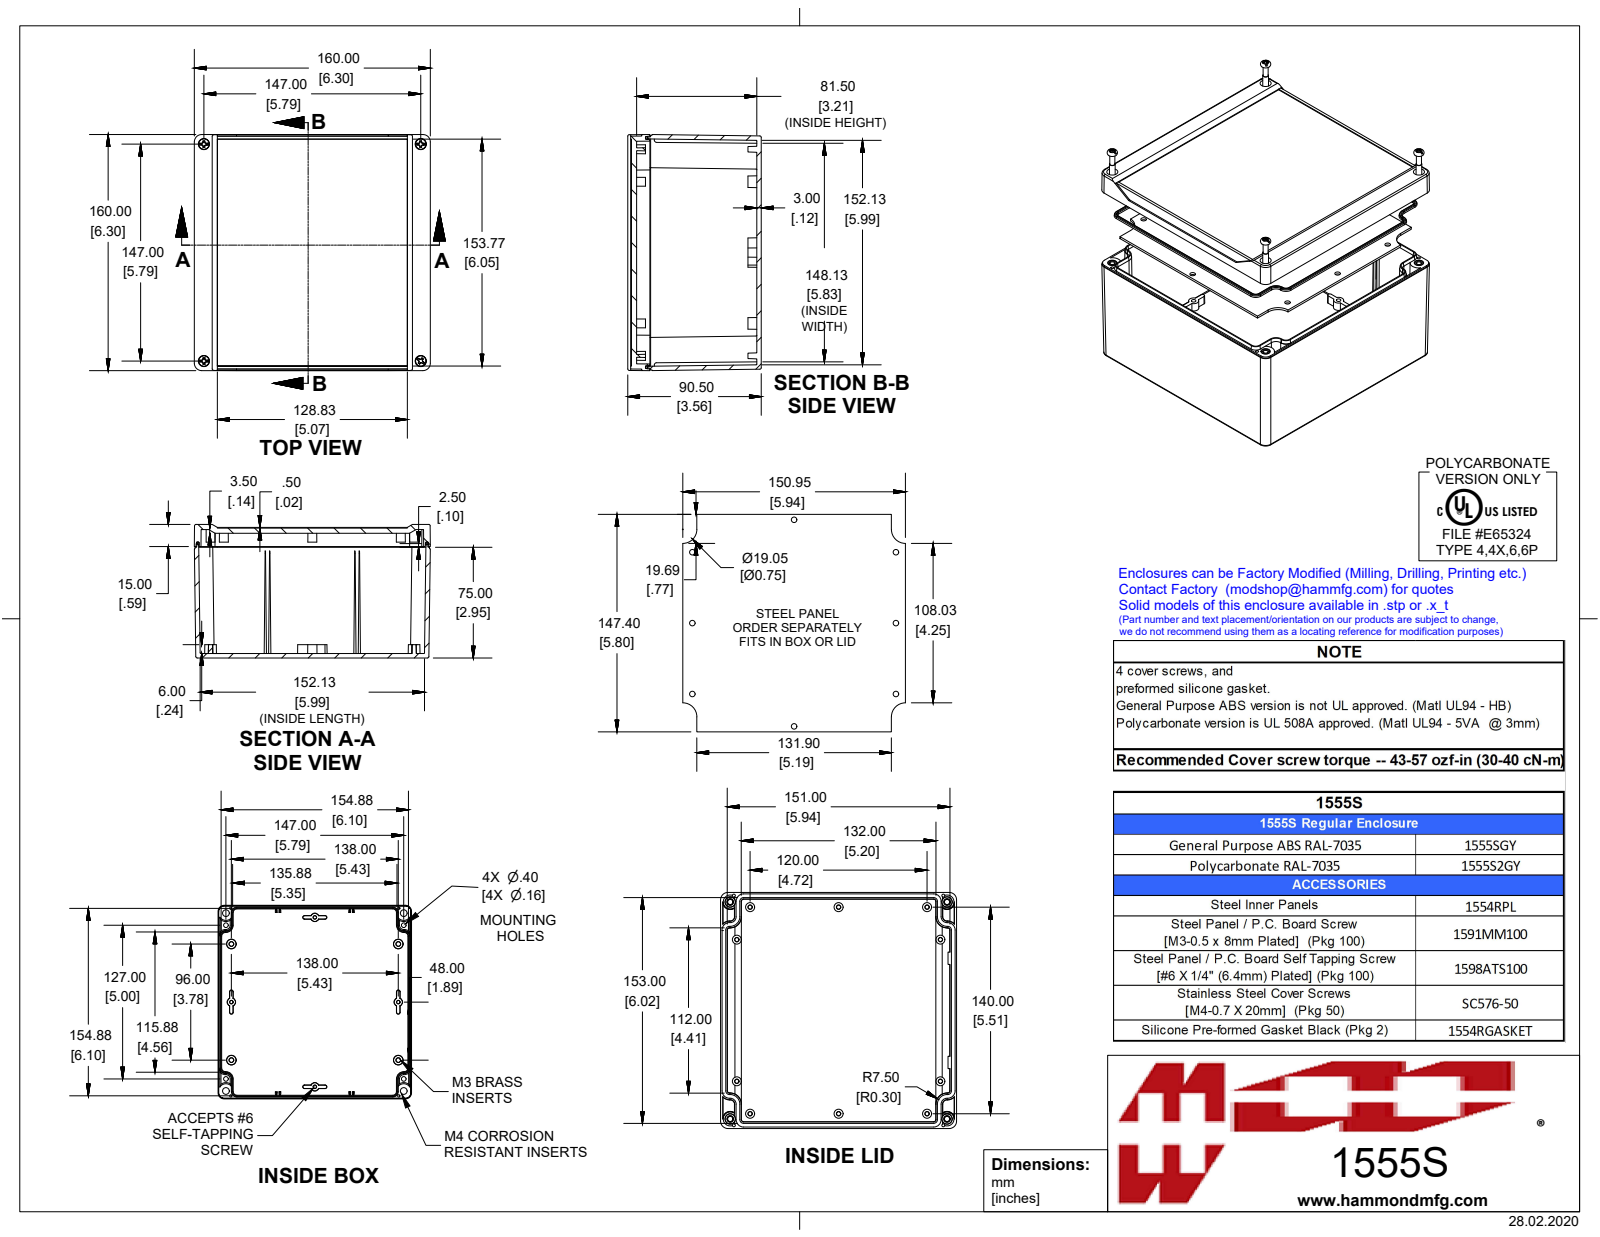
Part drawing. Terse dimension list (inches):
name: 1555S2GY
written by: SolidWorks 2019 (AUTOMOTIVE_DESIGN)
unit: in
bodies: 15 solids, 1396 faces (424 planar, 328 cylindrical, 644 other)
size: 6.299 × 6.299 × 3.563
volume: 21.69 in³; area: 379.9 in²
holes: 8× ⌀0.079, 4× ⌀0.097, 4× ⌀0.128, 4× ⌀0.138, 4× ⌀0.276
bosses: 4× ⌀0.25, 4× ⌀0.236, 4× ⌀0.218, 4× ⌀0.21, 4× ⌀0.19, 4× ⌀0.154, 4× ⌀0.153, 4× ⌀0.15
rounds: 32× R0.02, 8× R0.039, 8× R0.197, 4× R0.187, 2× R0.059
face distances: 0.118, 0.138, 3.209, 3.465, 3.346, 3.327, 0.059, 0.374, 0.098, 0.236
hole spacings: 0.197, 1.019, 1.177, 4.787, 4.955, 5.635, 5.691, 5.699
